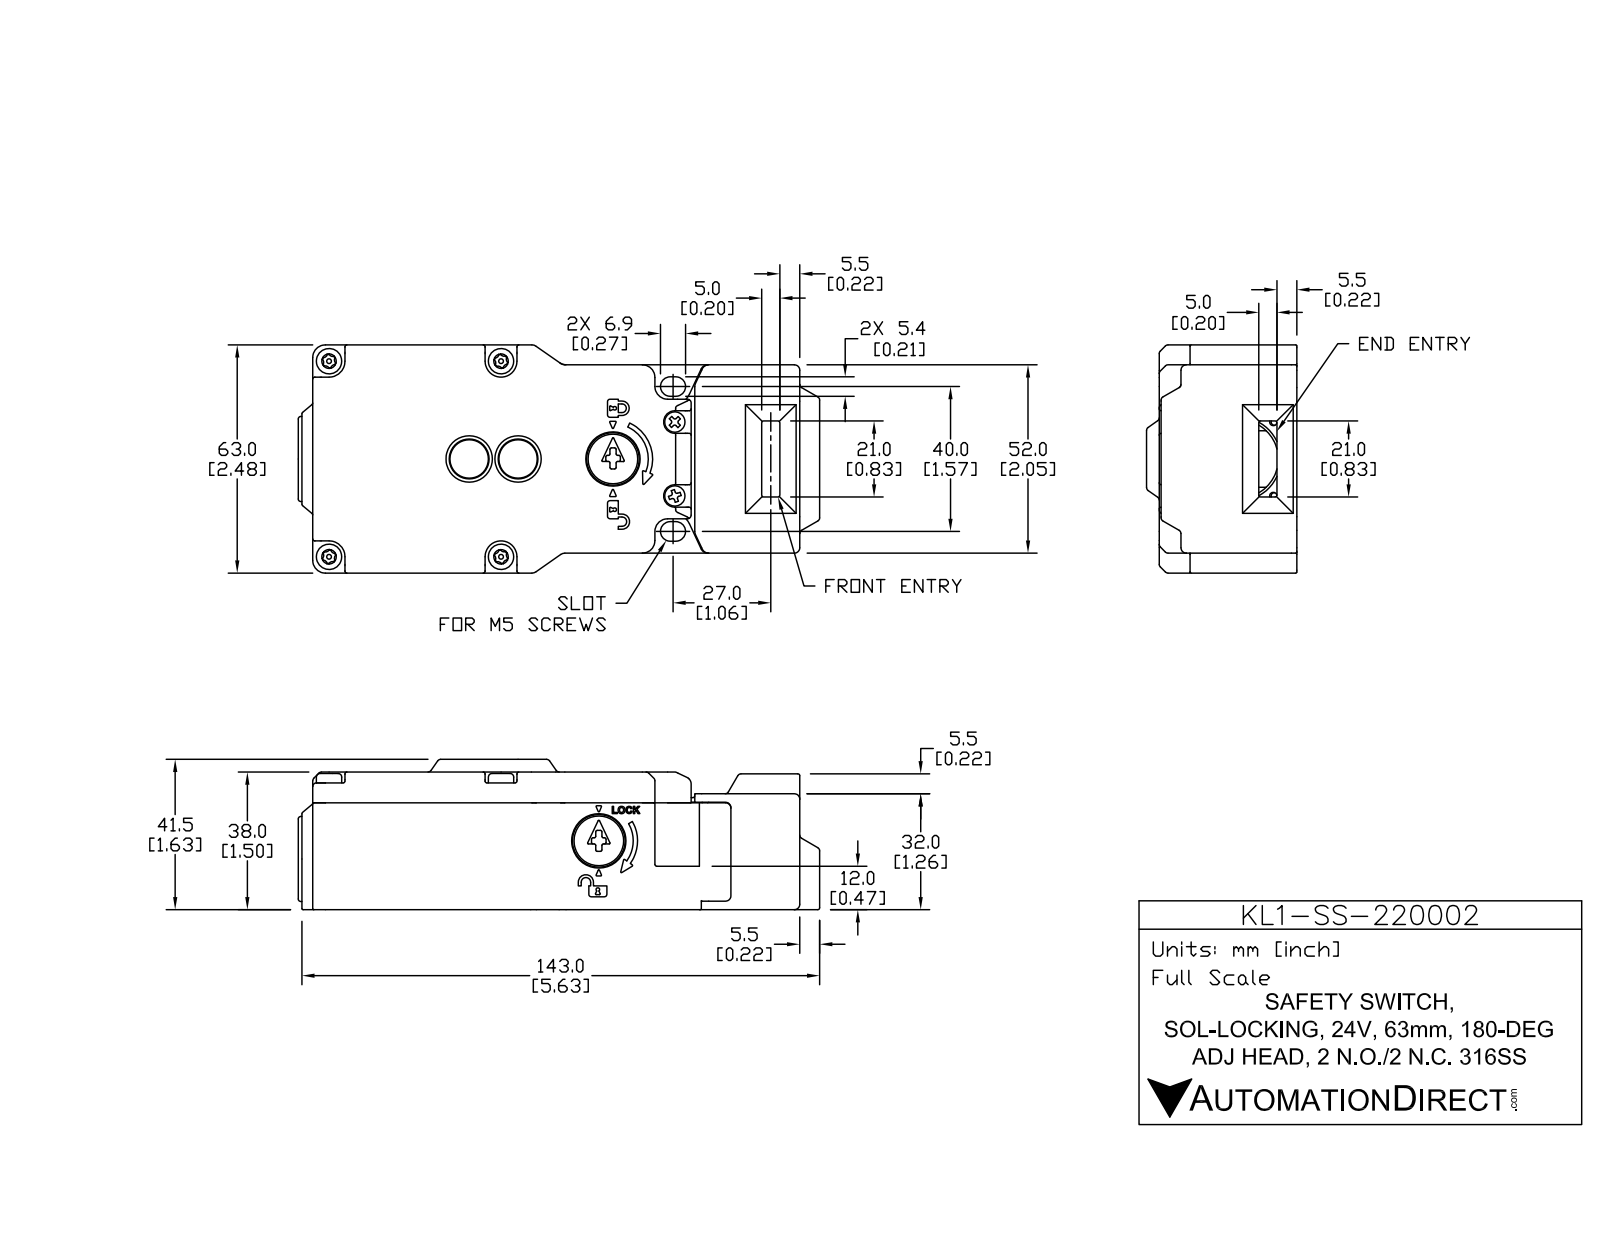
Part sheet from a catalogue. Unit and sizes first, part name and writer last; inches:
Units: inches
Overall size (bounding box): 5.669 × 2.48 × 1.634
Round holes (diameter × count): ⌀0.102 ×4, ⌀0.134 ×4, ⌀0.157 ×4, ⌀0.161 ×4, ⌀0.177 ×4, ⌀0.197 ×4, ⌀0.079 ×2, ⌀0.083 ×2, ⌀0.118 ×2, ⌀0.126 ×2, ⌀0.142 ×2, ⌀0.264 ×2
Round bosses / shafts (diameter × count): ⌀0.276 ×4, ⌀0.138 ×4, ⌀0.051 ×4, ⌀0.197 ×3, ⌀0.039 ×3, ⌀0.571 ×2, ⌀0.417 ×2, ⌀0.362 ×2
Partial cylindrical surfaces — rounded edges, fillets, slot ends (radius × count): R0.02 ×348, R0.012 ×126, R0.039 ×106, R0.008 ×30, R0.016 ×24, R0.059 ×16, R0.006 ×14, R0.028 ×12
Main face-to-face distances: 0.098, 0.118, 0.217, 1.496, 1.398, 1.402, 1.303, 0.094, 2.264, 2.146
Hole centre spacings: 0.404, 0.498, 0.515, 0.549, 0.784, 0.803, 1.079, 1.118
Volume: 6.348 in³ · Surface area: 118.8 in²
Bodies: 18 solids, 3047 faces (909 planar, 1225 cylindrical, 913 other)
Part name (STEP PRODUCT): KL1-SS-220002
STEP written by: SolidWorks 2017 (AUTOMOTIVE_DESIGN)
